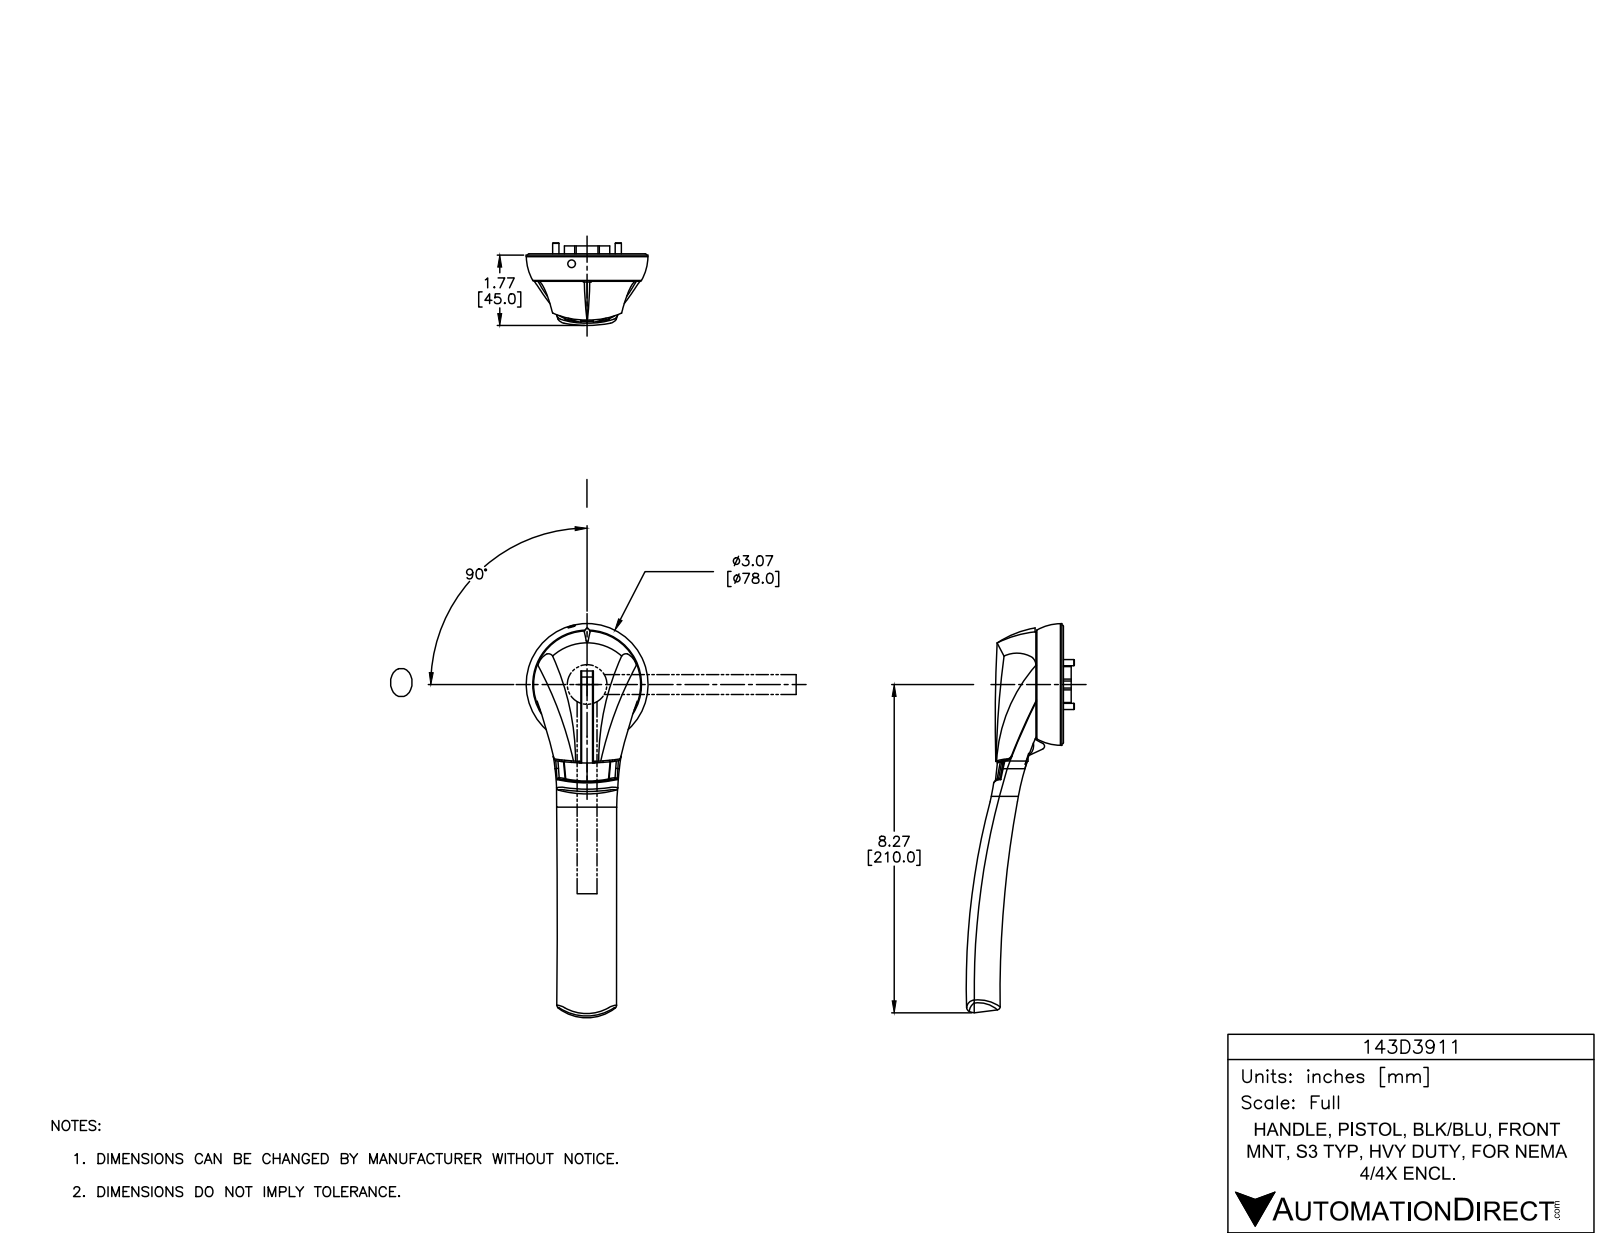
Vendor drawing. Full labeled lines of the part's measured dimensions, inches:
Part name (STEP PRODUCT): 143D3911
STEP written by: SolidWorks 2015 (AUTOMOTIVE_DESIGN)
Units: inches
Bodies: 8 solids, 1514 faces (806 planar, 544 cylindrical, 164 other)
Overall size (bounding box): 9.793 × 3.07 × 2.721
Volume: 12.91 in³ · Surface area: 100.4 in²
Round holes (diameter × count): ⌀0.157 ×6, ⌀0.339 ×4, ⌀0.425 ×4, ⌀0.03 ×3, ⌀0.169 ×2, ⌀0.362 ×2, ⌀0.118 ×1, ⌀0.189 ×1, ⌀2.992 ×1
Round bosses / shafts (diameter × count): ⌀0.02 ×11, ⌀0.335 ×4, ⌀0.315 ×4, ⌀0.089 ×3, ⌀0.069 ×3, ⌀0.228 ×2, ⌀2.819 ×1, ⌀2.701 ×1
Partial cylindrical surfaces — rounded edges, fillets, slot ends (radius × count): R0.01 ×221, R0.015 ×20, R0.034 ×20, R0.03 ×15, R0.039 ×4, R0.025 ×3, R5.437 ×3, R0.079 ×2
Main face-to-face distances: 0.024, 0.701, 0.713, 0.689, 0.035, 0.276, 0.102, 0.173, 0.244, 0.047
Hole centre spacings: 0.961, 0.309, 0.669, 1.098, 1.102, 1.203, 1.575, 1.881
